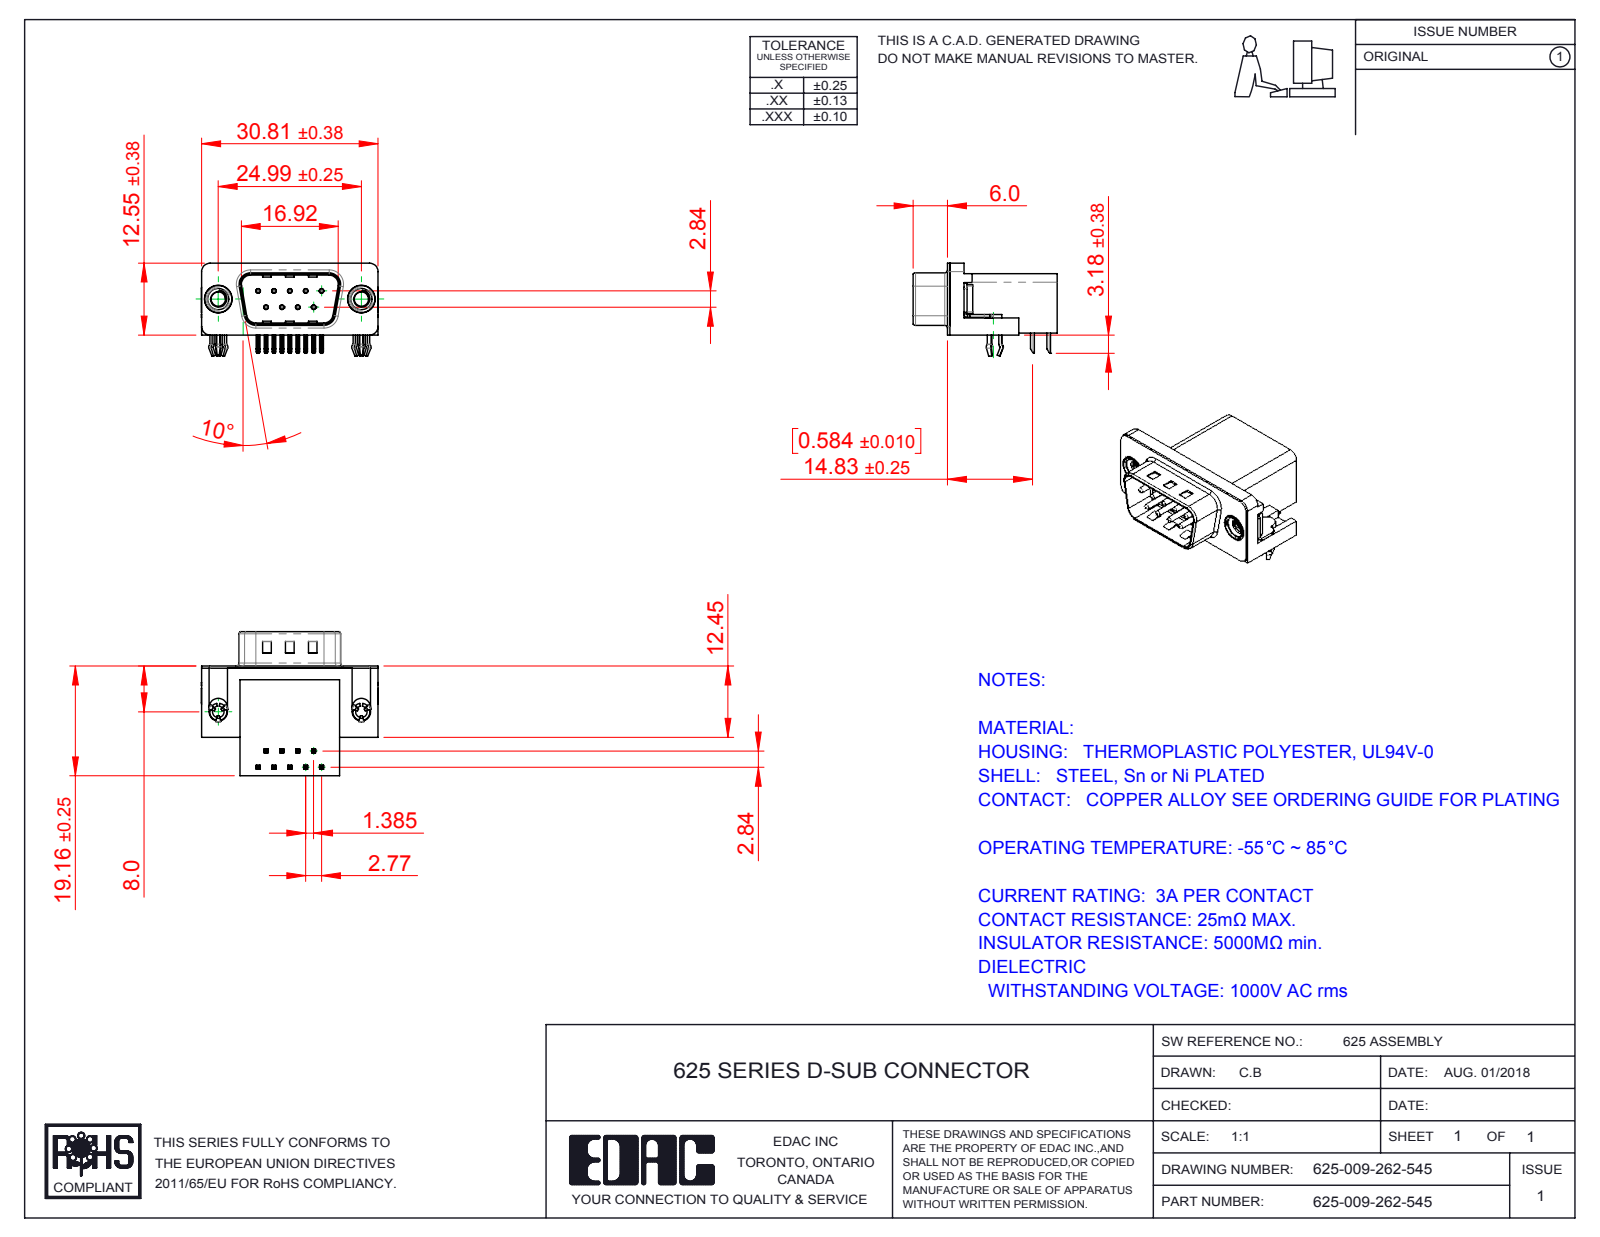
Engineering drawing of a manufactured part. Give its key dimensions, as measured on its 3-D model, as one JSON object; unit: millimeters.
{"part_name": "625 M3 Threaded Rivet; 625 Contact Bottom; 625 3 Prong Board Lock; 625 Contact Top (+3 more)", "step_written_by": "SolidWorks 2016 (CONFIG_CONTROL_DESIGN)", "units": "millimeters", "bodies": {"solids": 15, "faces": 1097, "planar": 611, "cylindrical": 327, "other": 159}, "overall_size": [30.89, 25.16, 16.25], "volume_mm3": 4479, "surface_area_mm2": 5016, "round_holes": [[0.35, 9], [0.8, 9], [2, 2], [2.5, 2], [4, 2], [4.8, 2], [5, 2]], "round_bosses_or_shafts": [[0.75, 9], [4.9, 2], [4.75, 2], [3.9, 2], [3, 2]], "partial_cylinders_radius": [[0.25, 48], [0.12, 18], [1, 16], [0.5, 9], [1.5, 8], [1.6, 8], [0.9, 4], [2, 4]], "face_to_face_distances": [0.4, 10.34, 18.76, 19.16, 2.9, 16.26, 2.5, 0.35, 10.69, 6.7], "hole_center_spacings": [3.16, 2.77, 5.54, 5.03, 5.04, 8.31, 7.48, 7.49]}
